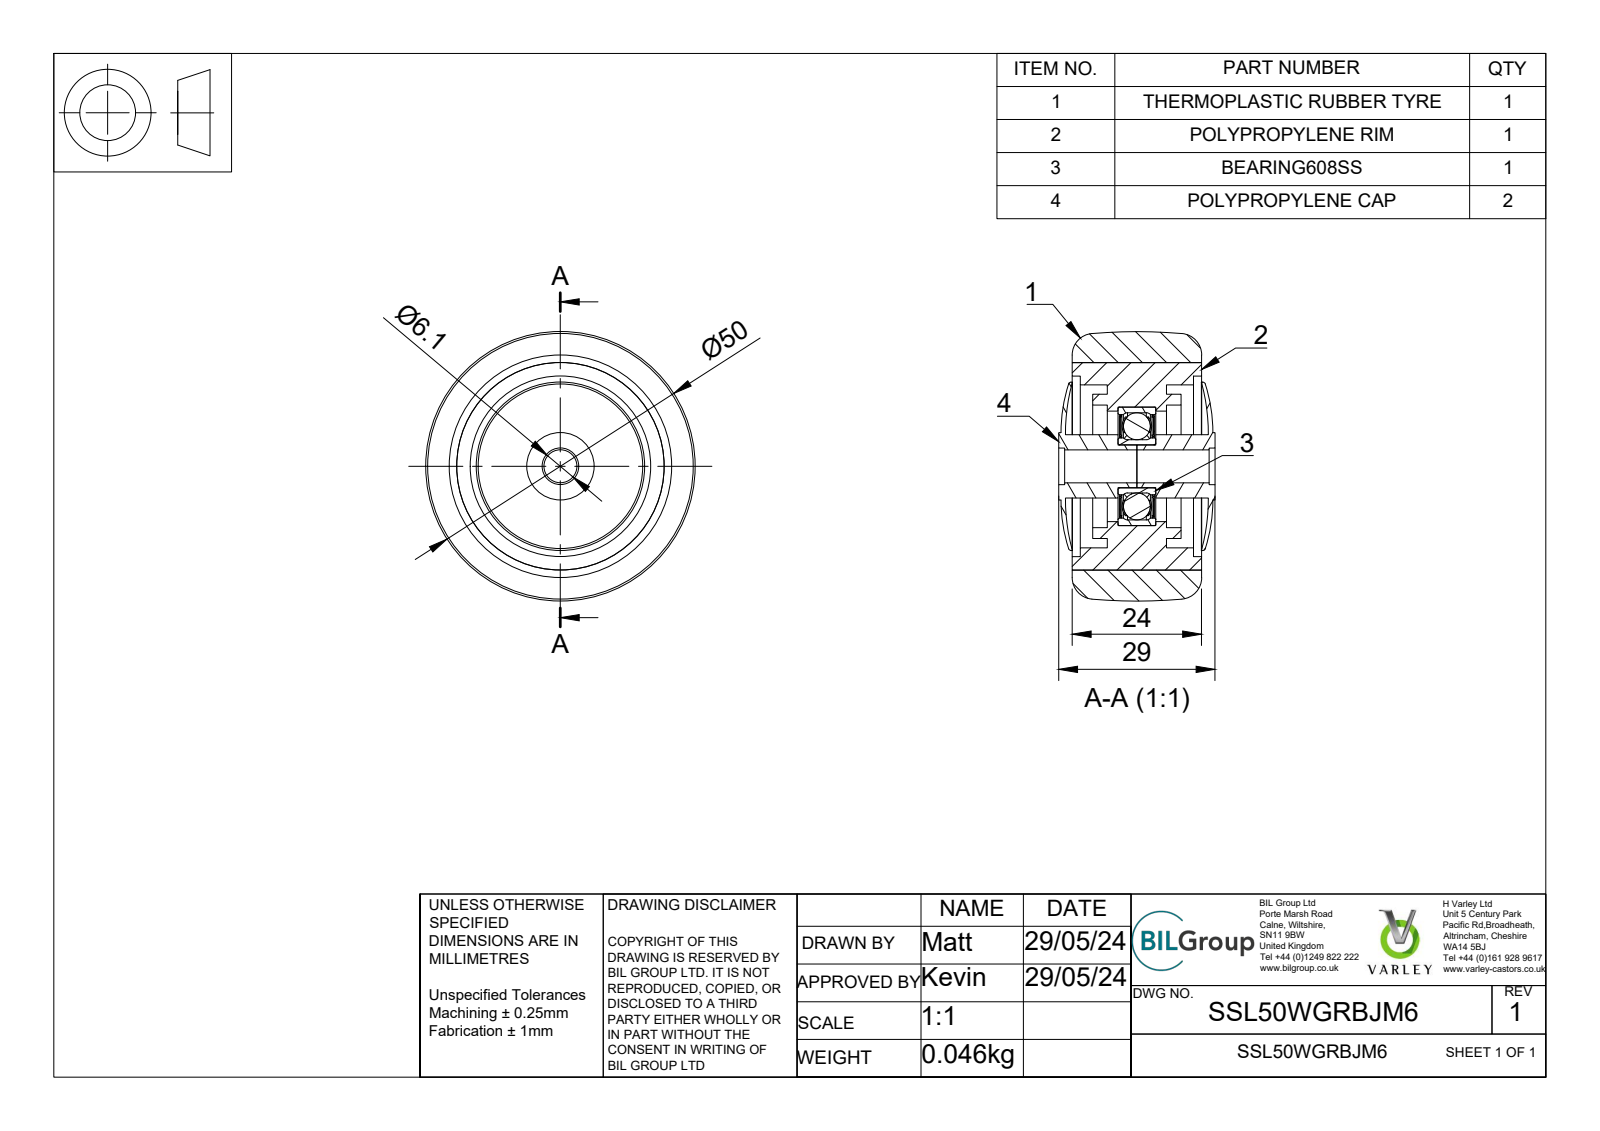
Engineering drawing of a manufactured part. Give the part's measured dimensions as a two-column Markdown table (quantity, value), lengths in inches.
| quantity | value |
| --- | --- |
| part name | SSL50WGRBJM6 v2; POLYPROPYLENE RIM; THERMOPLASTIC RUBBER TYRE; CAP (+7 more) |
| STEP written by | Autodesk Translation Framework v13.14.0.145 (AUTOMOTIVE_DESIGN) |
| units | inches |
| bodies | 15 solids, 144 faces (50 planar, 47 cylindrical, 47 other) |
| overall size | 1.969 × 1.969 × 1.142 |
| volume | 2.238 in³ |
| surface area | 36.23 in² |
| round holes (diameter × count) | 0.24 × 1, 0.268 × 1, 0.315 × 1, 0.415 × 1, 0.441 × 1, 0.502 × 1, 0.72 × 1, 0.756 × 1, 0.783 × 1, 0.807 × 1, 0.866 × 1, 0.896 × 1 |
| round bosses / shafts (diameter × count) | 1.23 × 1, 1.053 × 1, 0.736 × 1, 0.721 × 1, 0.492 × 1, 0.463 × 1, 0.457 × 1, 0.389 × 1 |
| main face-to-face distances | 0.256, 0.344, 0.433, 0.248, 0.354, 0.276, 0.443, 0.451, 0.61, 0.689 |
